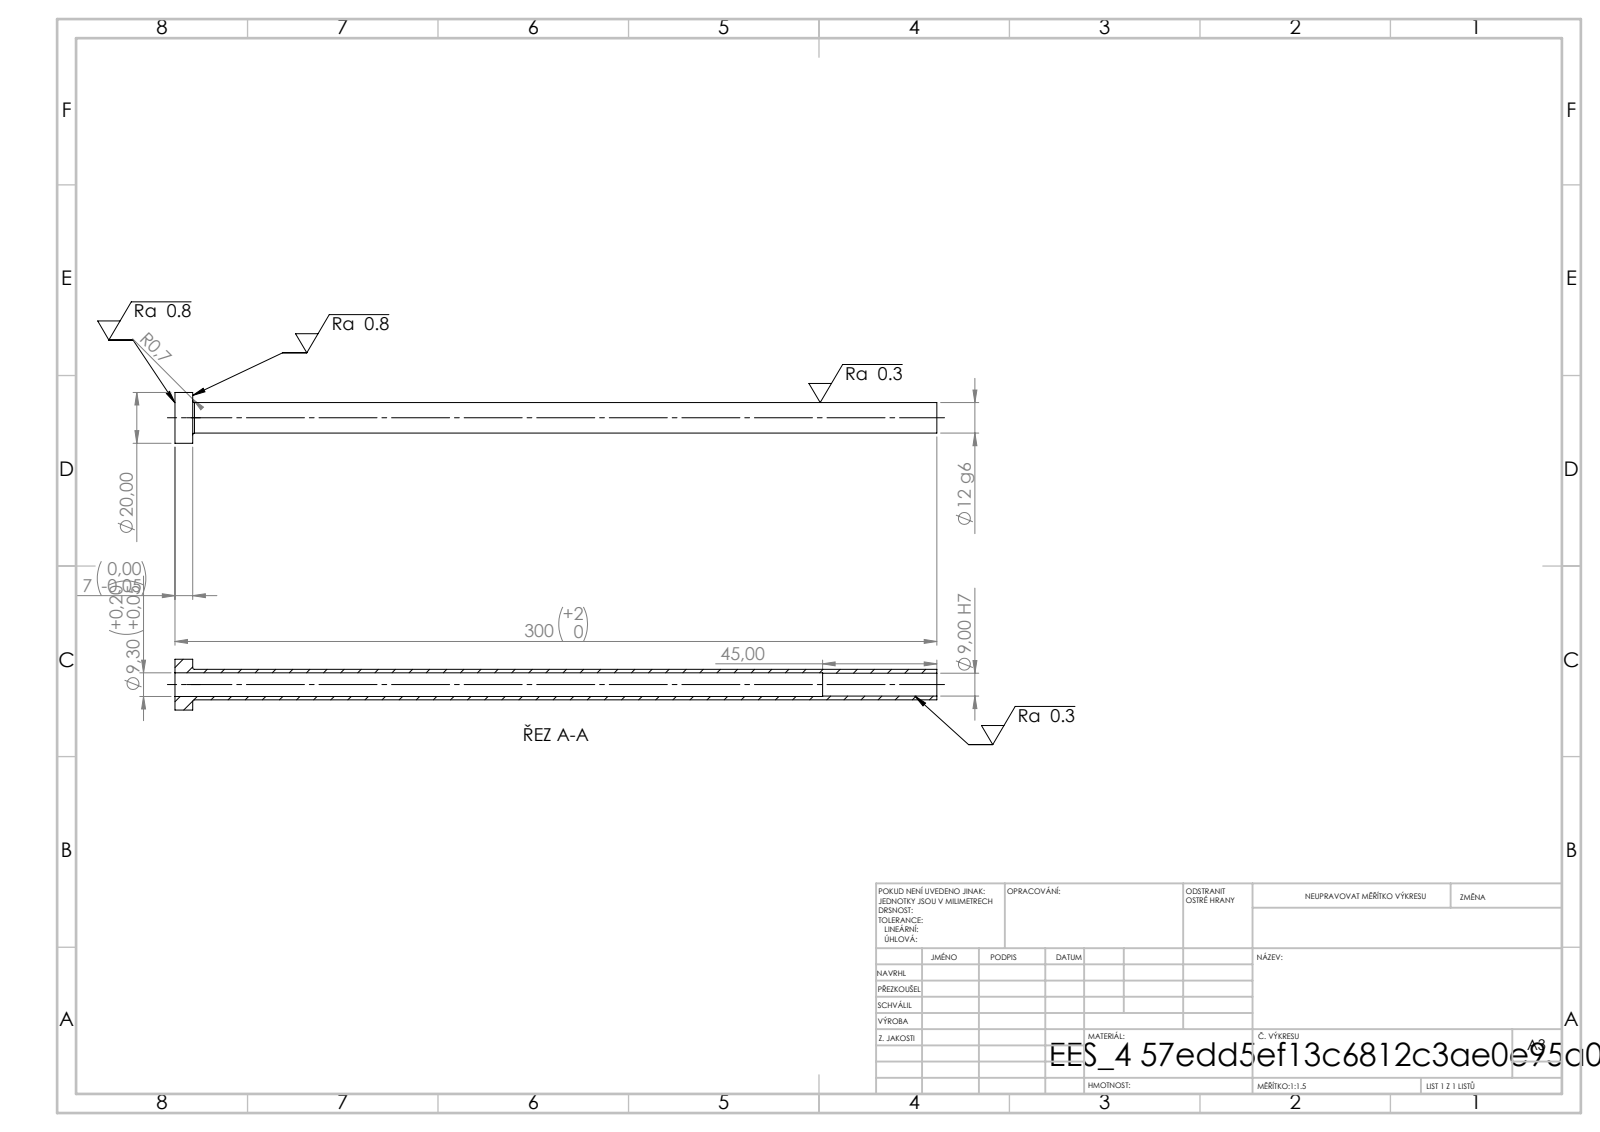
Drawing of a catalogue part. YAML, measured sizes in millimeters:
step_written_by: "SolidWorks 2019 (CONFIG_CONTROL_DESIGN)"
units: millimeters
bodies: {solids: 1, faces: 14, planar: 4, cylindrical: 8, other: 2}
overall_size: [300, 20, 20]
volume: 15156
surface_area: 20698
round_holes:
  - {diameter: 9, count: 1}
  - {diameter: 9.3, count: 1}
round_bosses_or_shafts:
  - {diameter: 20, count: 1}
  - {diameter: 12, count: 1}
face_to_face_distances: [7, 300, 293, 255, 248, 45]
